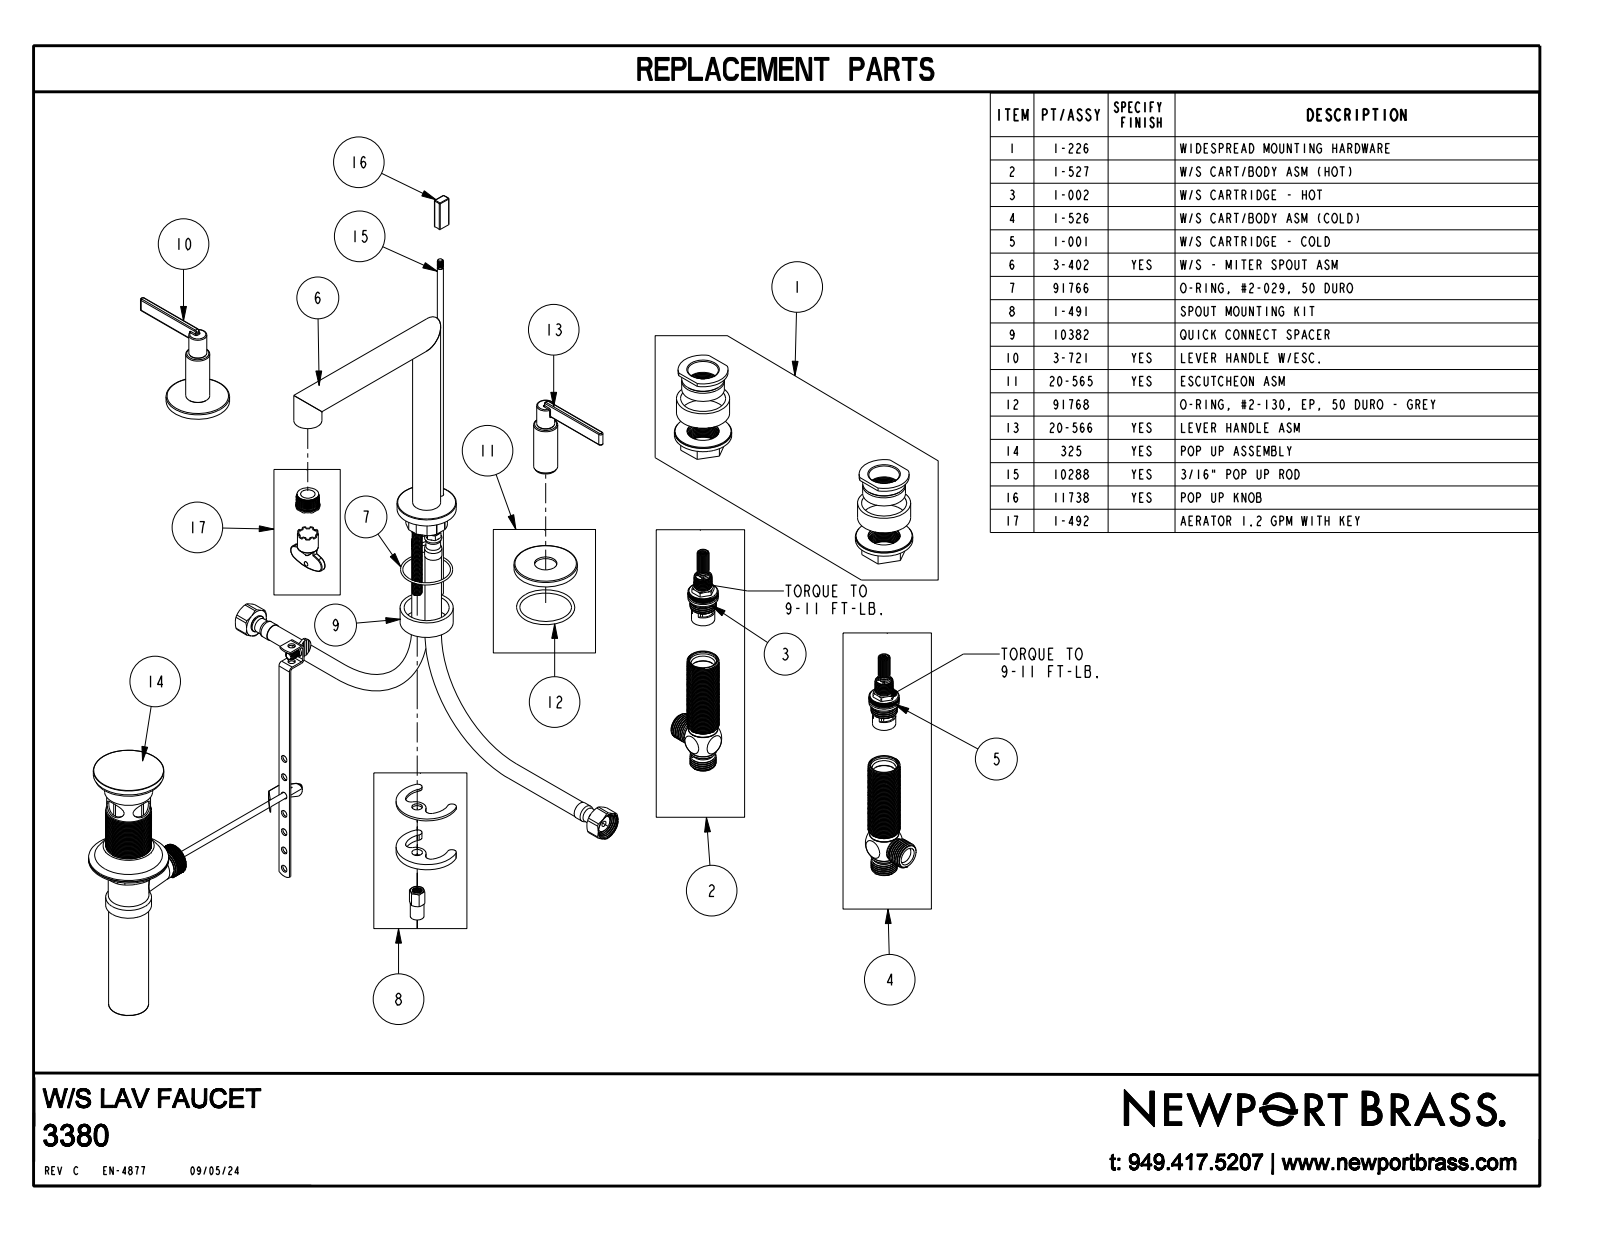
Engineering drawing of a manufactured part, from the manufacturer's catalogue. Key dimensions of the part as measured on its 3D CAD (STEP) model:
Part name (STEP PRODUCT): 3380
STEP written by: CREO PARAMETRIC BY PTC INC, 2019352 (CONFIG_CONTROL_DESIGN)
Units: inches
Bodies: 4 solids, 139 faces (33 planar, 64 cylindrical, 42 other)
Overall size (bounding box): 13 × 7.089 × 6.678
Volume: 11.45 in³ · Surface area: 74.34 in²
Round holes (diameter × count): ⌀0.721 ×1
Round bosses / shafts (diameter × count): ⌀0.875 ×3, ⌀1.98 ×2, ⌀0.75 ×2, ⌀0.73 ×2, ⌀0.563 ×2, ⌀0.51 ×2, ⌀1.85 ×1
Partial cylindrical surfaces — rounded edges, fillets, slot ends (radius × count): R0.03 ×16, R0.02 ×6, R0.06 ×2, R0.075 ×2, R0.47 ×1, R0.876 ×1
Main face-to-face distances: 0.2, 0.25, 0.05, 0.15, 2.701, 2.501, 2.451, 6.094, 5.894, 5.844
